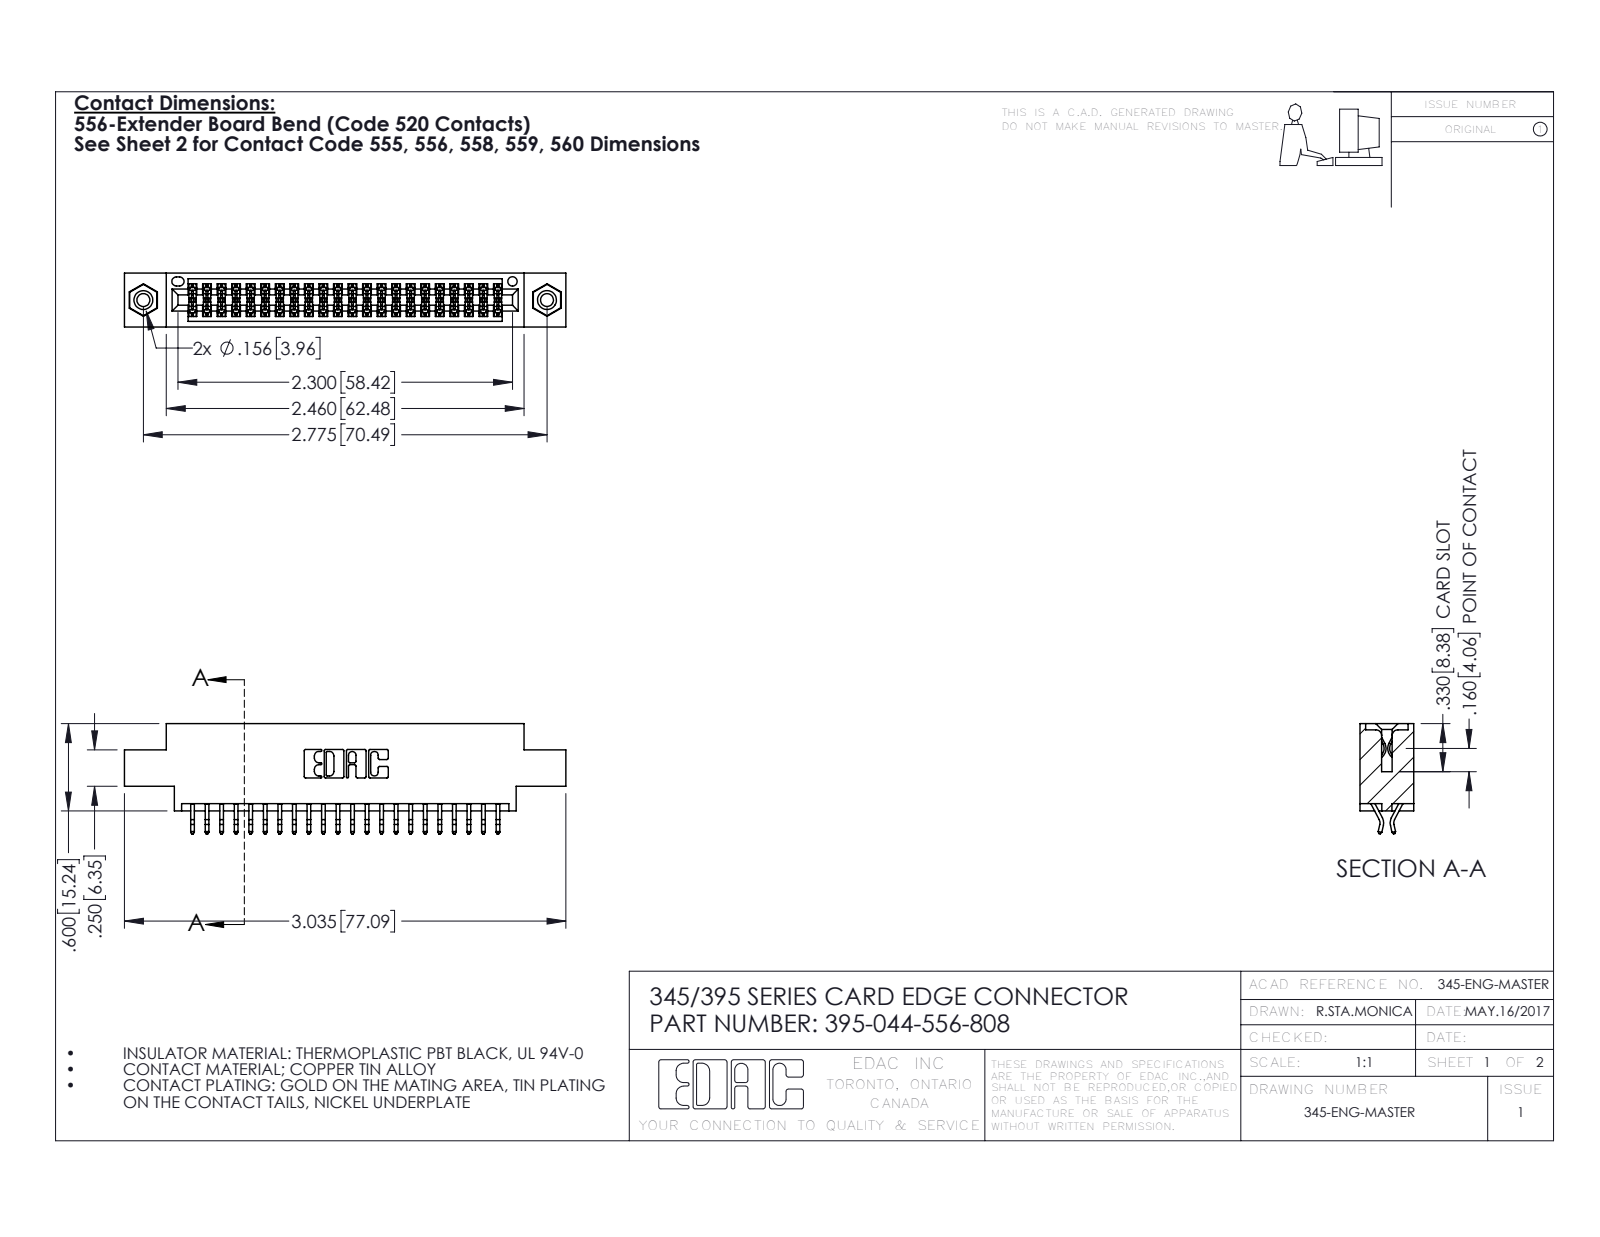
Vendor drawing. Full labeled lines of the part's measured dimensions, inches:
Part name (STEP PRODUCT): 345-250-001_345-250-003-102; 345-292-001_556 Tail; 395-044-556-808; 345 Part_0.170 Offset - 0.156 Dia-TI
STEP written by: SolidWorks 2016 (CONFIG_CONTROL_DESIGN)
Units: inches
Bodies: 47 solids, 2654 faces (1744 planar, 894 cylindrical, 16 other)
Overall size (bounding box): 3.035 × 0.757 × 0.37
Volume: 0.438 in³ · Surface area: 16.04 in²
Round holes (diameter × count): ⌀0.089 ×2, ⌀0.125 ×2, ⌀0.156 ×2, ⌀0.064 ×1
Round bosses / shafts (diameter × count): ⌀0.155 ×2
Partial cylindrical surfaces — rounded edges, fillets, slot ends (radius × count): R0.006 ×66, R0.01 ×22, R0.007 ×6, R0.031 ×6, R0.026 ×3, R0.01 ×2, R0.014 ×2, R0.019 ×2
Main face-to-face distances: 0.072, 0.298, 0.37, 0.2, 0.025, 0.098, 0.272, 0.225, 0.175, 0.149
Hole centre spacings: 0.27, 2.541, 2.775
